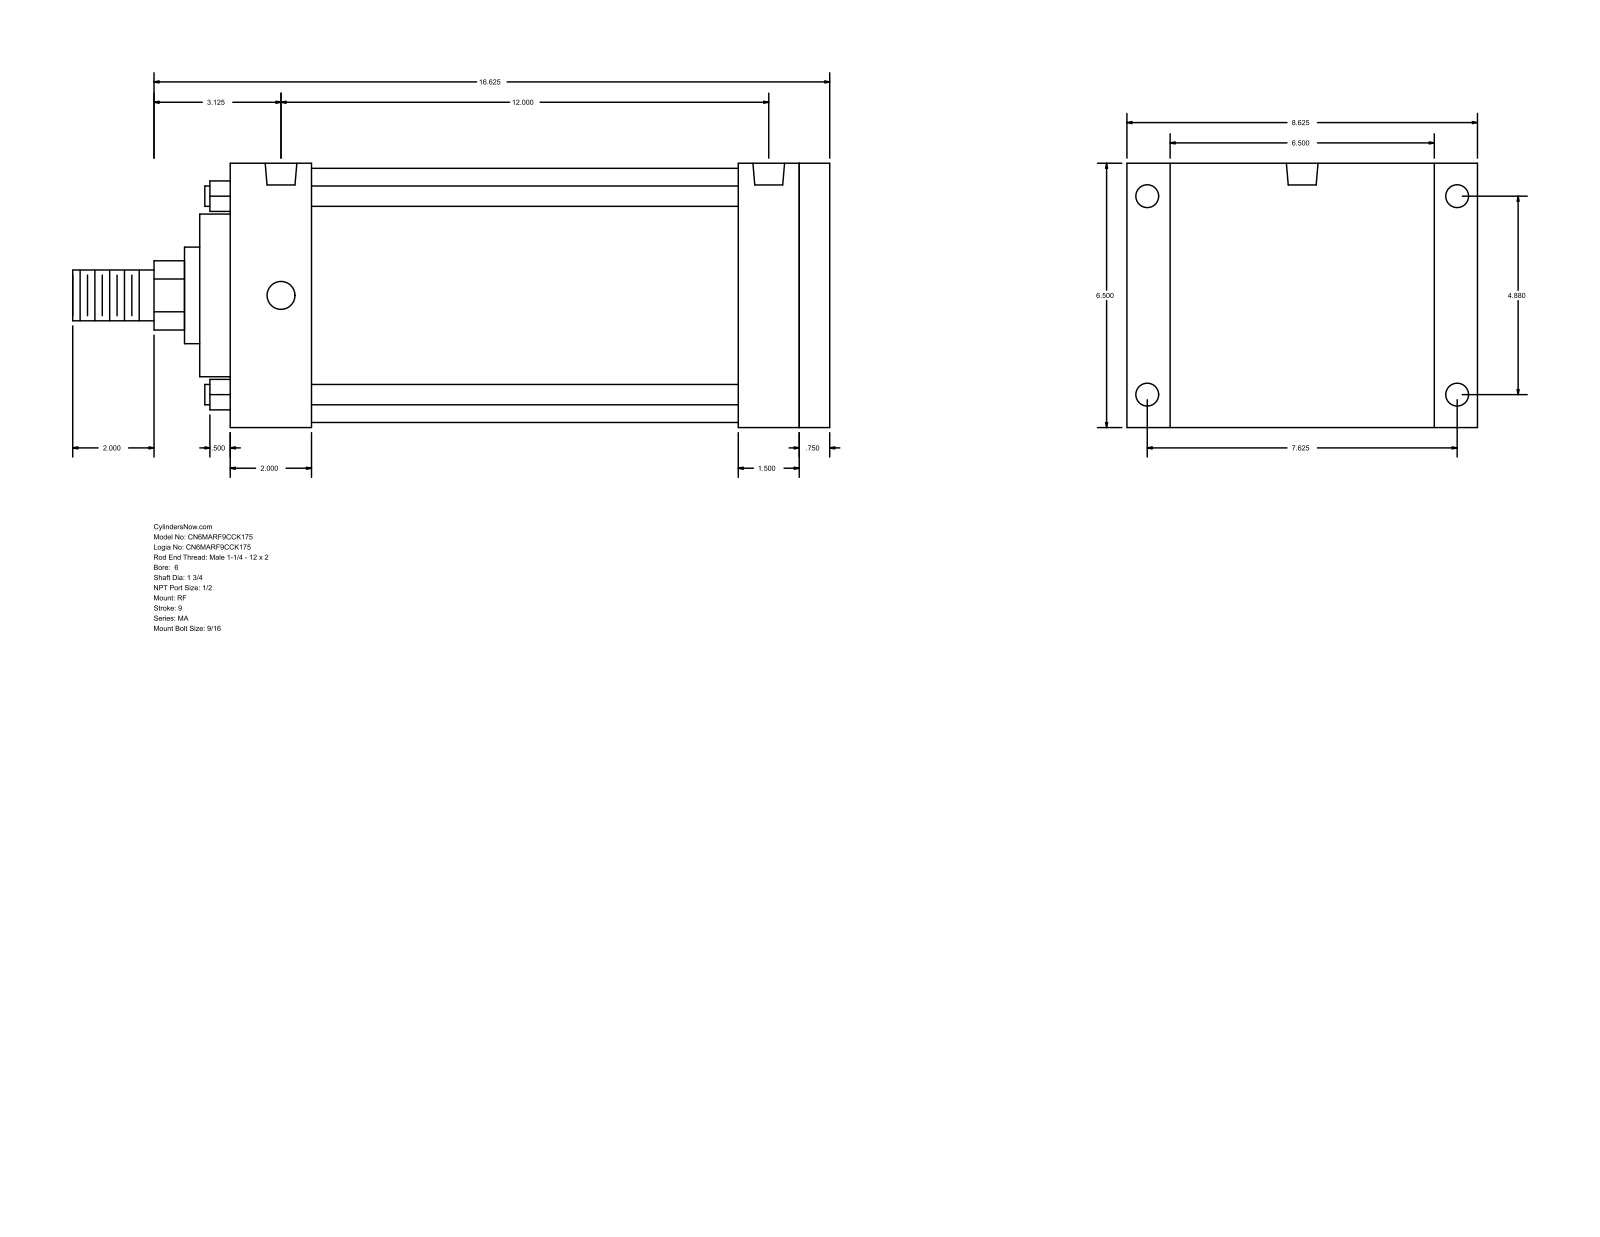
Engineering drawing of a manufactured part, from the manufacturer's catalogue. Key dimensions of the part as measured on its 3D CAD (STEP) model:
Part name (STEP PRODUCT): MA_RF__0600_1.75
STEP written by: GSSL Pune (CONFIG_CONTROL_DESIGN)
Units: millimetres
Bodies: 0 solids, 94 faces (65 planar, 29 cylindrical, 0 other)
Overall size (bounding box): 473.07 × 219.07 × 165.1
Round holes (diameter × count): ⌀14.29 ×4, ⌀17.46 ×4, ⌀19.77 ×2
Round bosses / shafts (diameter × count): ⌀12.7 ×4, ⌀158.75 ×1, ⌀101.6 ×1, ⌀60.33 ×1, ⌀44.45 ×1, ⌀31.75 ×1
Partial cylindrical surfaces — rounded edges, fillets, slot ends (radius × count): R21.63 ×1
Main face-to-face distances: 165.1, 374.65, 19.04, 355.61, 50.8, 19.05, 304.81, 323.85, 317.5, 266.7
Hole centre spacings: 123.96, 193.68, 229.95, 304.8
